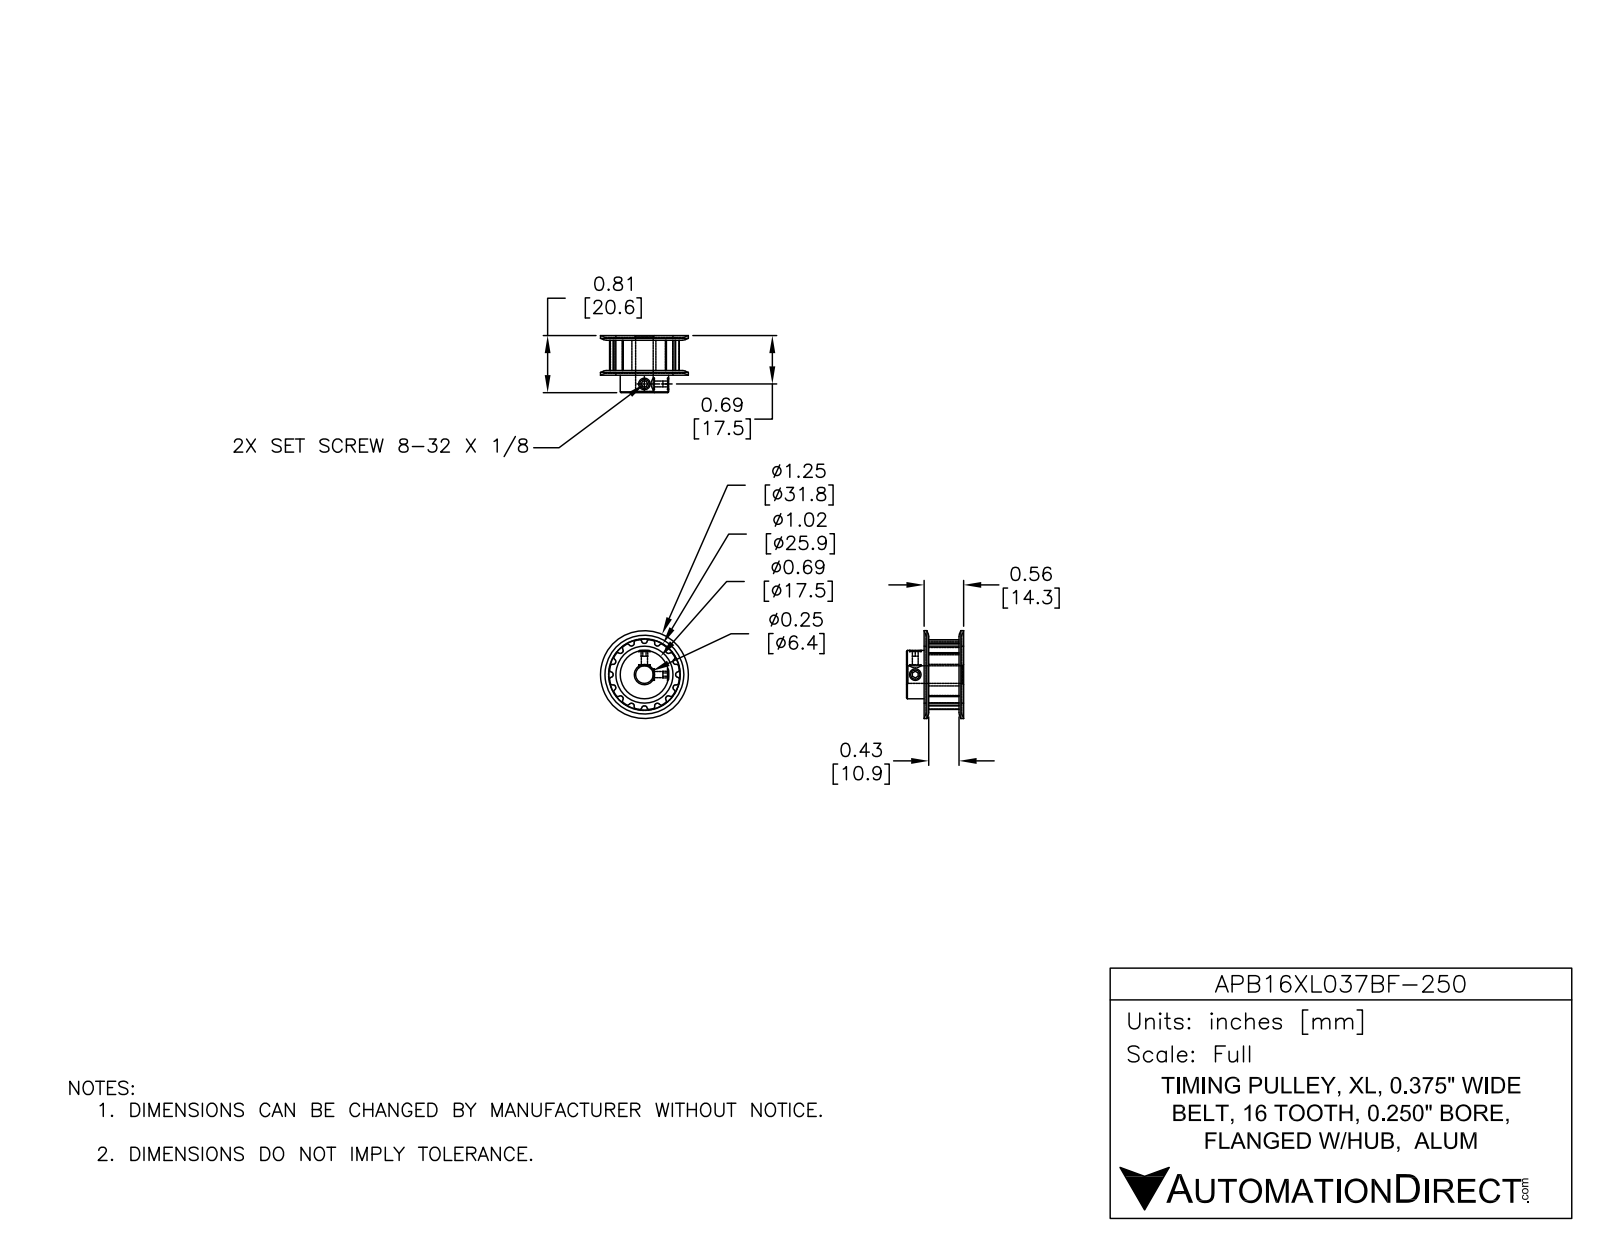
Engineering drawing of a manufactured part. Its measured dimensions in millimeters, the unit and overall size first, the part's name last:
Units: millimetres
Overall size (bounding box): 31.8 × 31.8 × 20.7
Round holes (diameter × count): ⌀2.2 ×2, ⌀6.4 ×1
Round bosses / shafts (diameter × count): ⌀17.5 ×1
Partial cylindrical surfaces — rounded edges, fillets, slot ends (radius × count): R0.4 ×64, R11.3 ×1
Main face-to-face distances: 12.6, 0.8, 13.4, 20.7, 19.8, 7.2, 25.4, 8.4, 11.7, 8.1
Volume: 7 600 mm³ · Surface area: 4 361 mm²
Bodies: 1 solid, 178 faces (54 planar, 102 cylindrical, 22 other)
Part name (STEP PRODUCT): APB16XL037BF-250
STEP written by: SolidWorks 2014 (AUTOMOTIVE_DESIGN)
